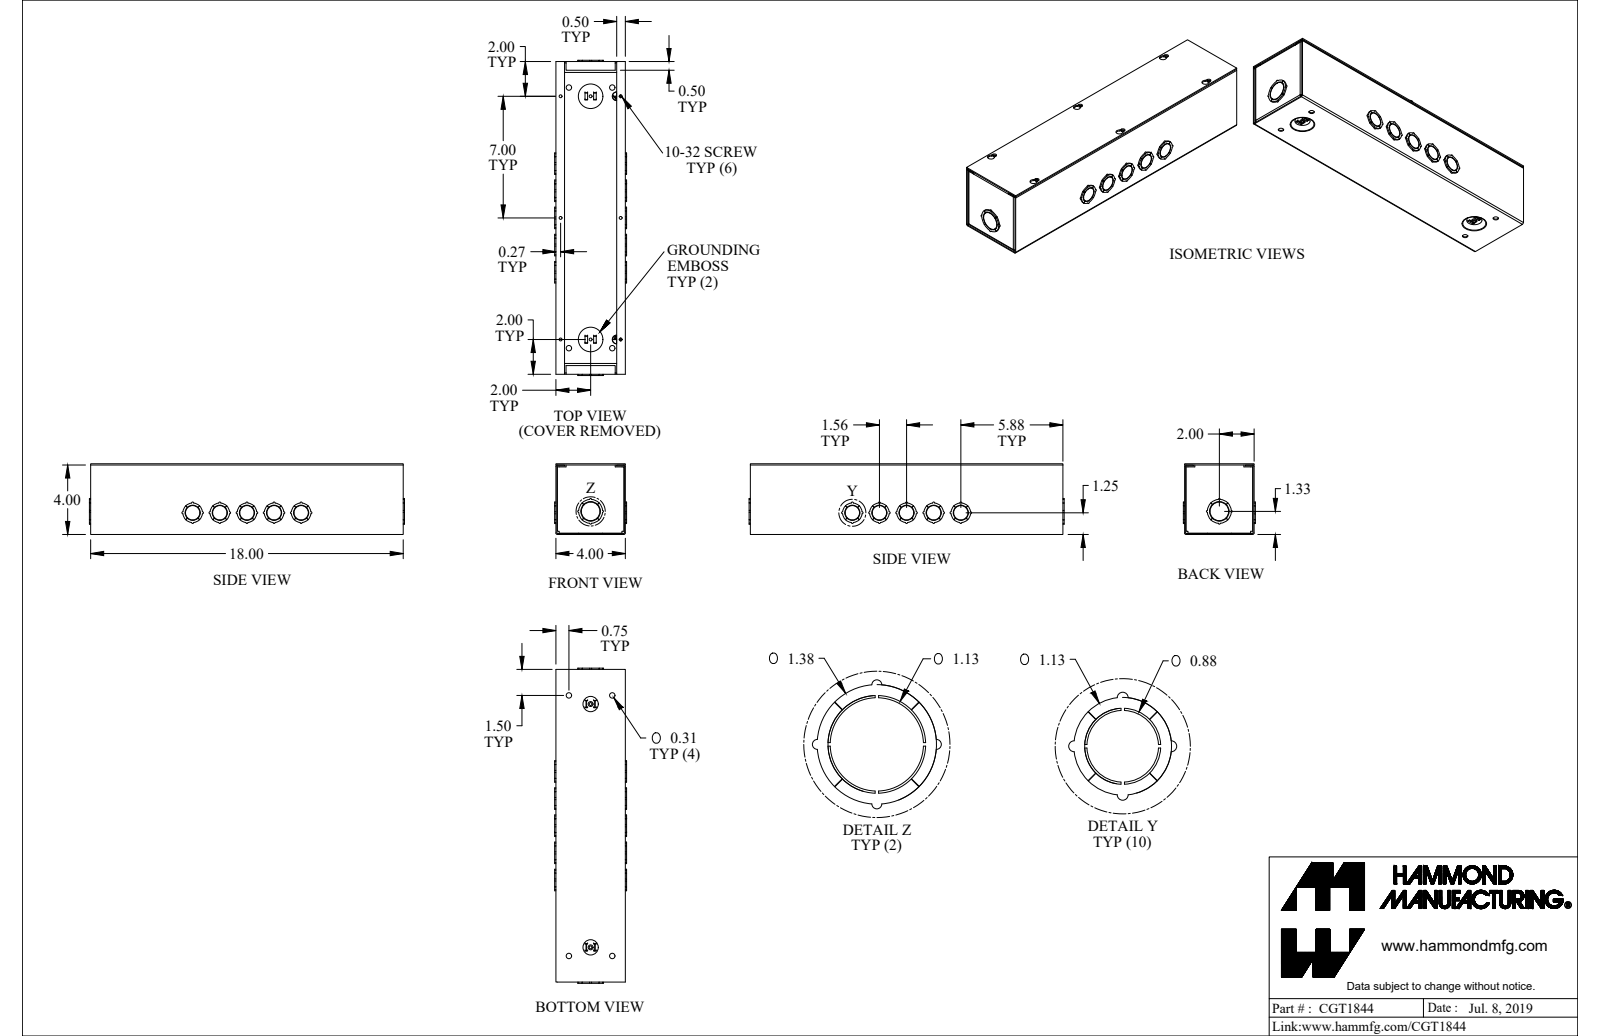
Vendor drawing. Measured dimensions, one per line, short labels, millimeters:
name: CGT1844
written by: SolidWorks 2021 (AUTOMOTIVE_DESIGN)
unit: mm
bodies: 6 solids, 788 faces (412 planar, 362 cylindrical, 14 other)
size: 460.9 × 107.9 × 105.3
volume: 364 100 mm³; area: 456 200 mm²
holes: 8× ⌀4.3, 5× ⌀22.2, 4× ⌀7.9, 2× ⌀12.7, 1× ⌀28.6
bosses: 5× ⌀28.6, 5× ⌀21, 2× ⌀12.5, 2× ⌀7.2, 2× ⌀4.8, 1× ⌀34.9, 1× ⌀27.3, 1× ⌀9.5
rounds: 20× R1.6, 8× R0.9, 8× R1.4, 8× R2.7, 6× R3.2, 6× R5.2, 4× R0.7, 4× R1.4
face distances: 1.4, 100.2, 101.6, 1.8, 98.7, 103.4, 102, 455.4, 3.3, 457.2
hole spacings: 17.6, 34.2, 43.9, 76.8, 177.8, 183.2, 190.9, 198.3
